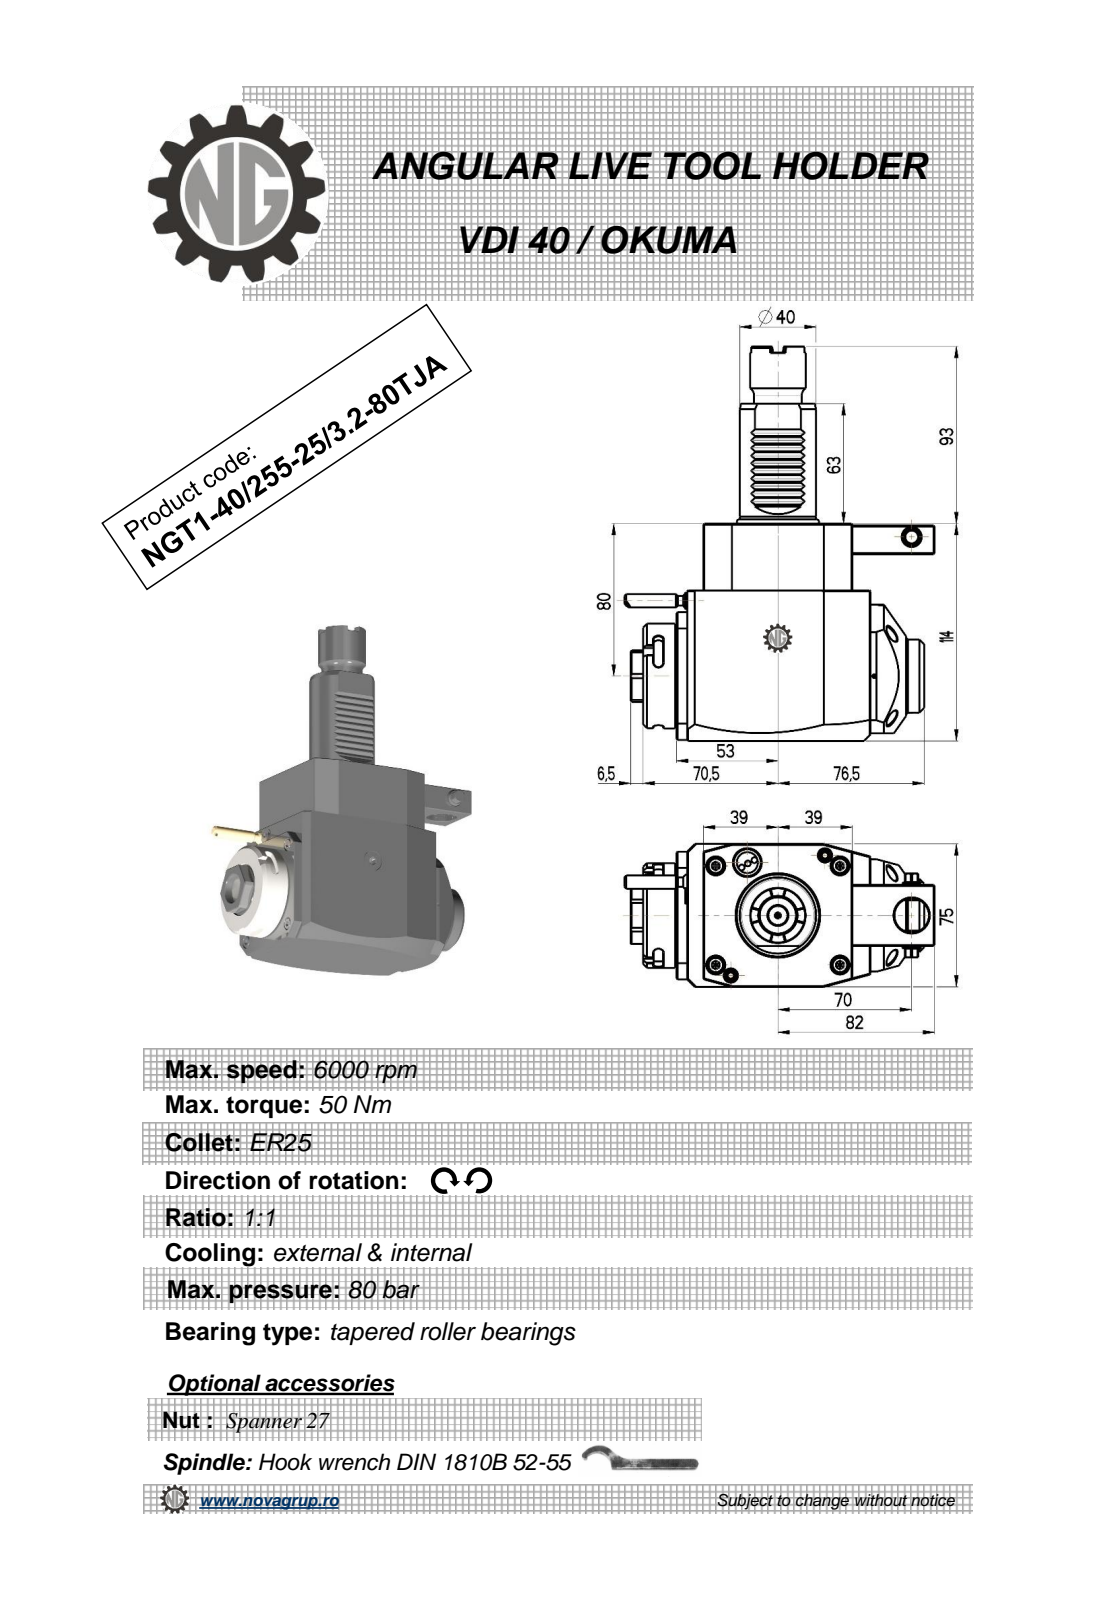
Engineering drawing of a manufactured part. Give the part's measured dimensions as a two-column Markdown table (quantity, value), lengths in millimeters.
| quantity | value |
| --- | --- |
| part name | NGT1_40_255_25_3_2_80TJA |
| STEP written by | PRO/ENGINEER BY PARAMETRIC TECHNOLOGY CORPORATION, 2010280 (CONFIG_CONTROL_DESIGN) |
| units | millimeters |
| bodies | 1 solid, 390 faces (196 planar, 86 cylindrical, 108 other) |
| overall size | 207 × 162.33 × 75 |
| volume | 991 521 mm³ |
| surface area | 76 017 mm² |
| round holes (diameter × count) | 18 × 2, 2.5 × 1, 3 × 1, 9.5 × 1 |
| round bosses / shafts (diameter × count) | 8.96 × 2, 55 × 1, 48 × 1, 40 × 1, 38.5 × 1, 29 × 1, 25 × 1, 10 × 1 |
| partial cylindrical surfaces (radius × count) | 0.3 × 10, 2.5 × 6, 180 × 2, 0.5 × 1, 3.85 × 1, 4.25 × 1, 10 × 1, 15 × 1 |
| main face-to-face distances | 75, 114, 14, 17.5, 109.5, 79, 92, 78, 31.5, 98 |
| hole center spacings | 37.35, 43.2, 72.5 |
